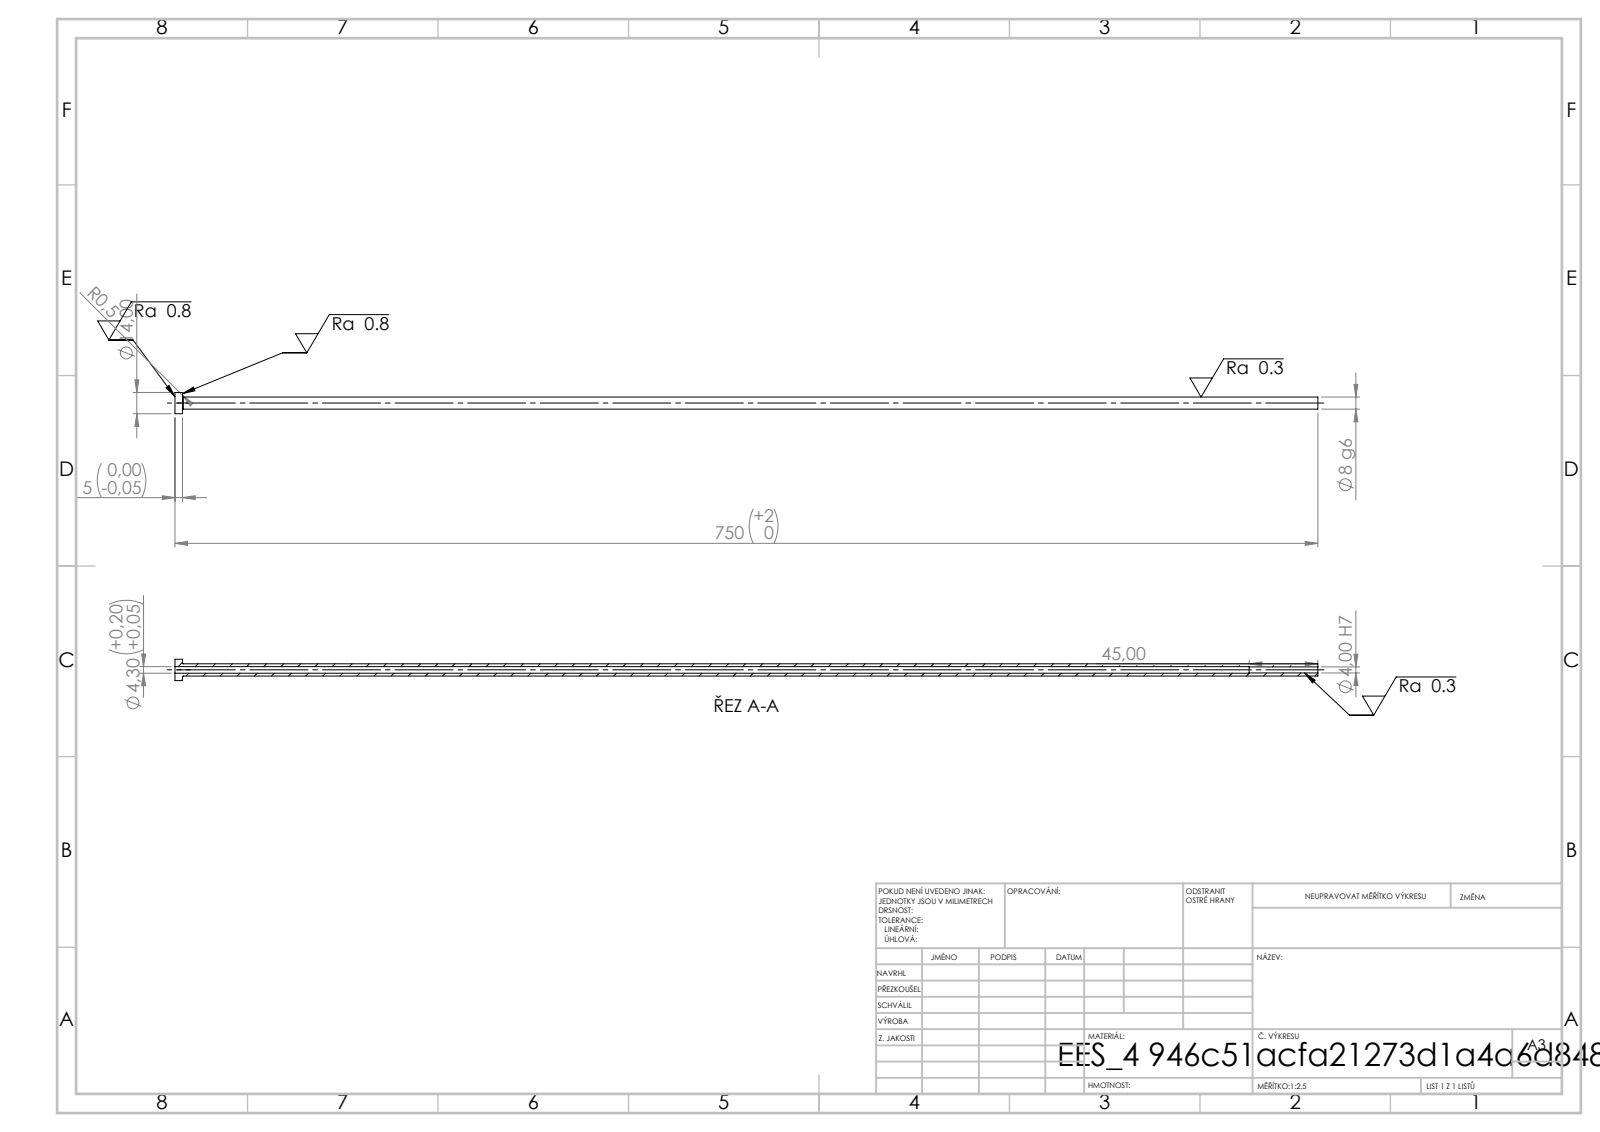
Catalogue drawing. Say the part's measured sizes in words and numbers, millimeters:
Its 3-D file was written by "SolidWorks 2019 (CONFIG_CONTROL_DESIGN)". It is 1 solid with 14 faces: 4 planar, 8 cylindrical and 2 other. Overall it measures 750 by 14 by 14 millimeters. Its volume is 27 415 cubic millimeters and its surface area 29 310 square millimeters. Round holes: 1 of diameter 4, 1 of diameter 4.3. Round bosses or shafts: 1 of diameter 14, 1 of diameter 8. The main face-to-face distances are 5, 750, 745, 705, 700, 45.
